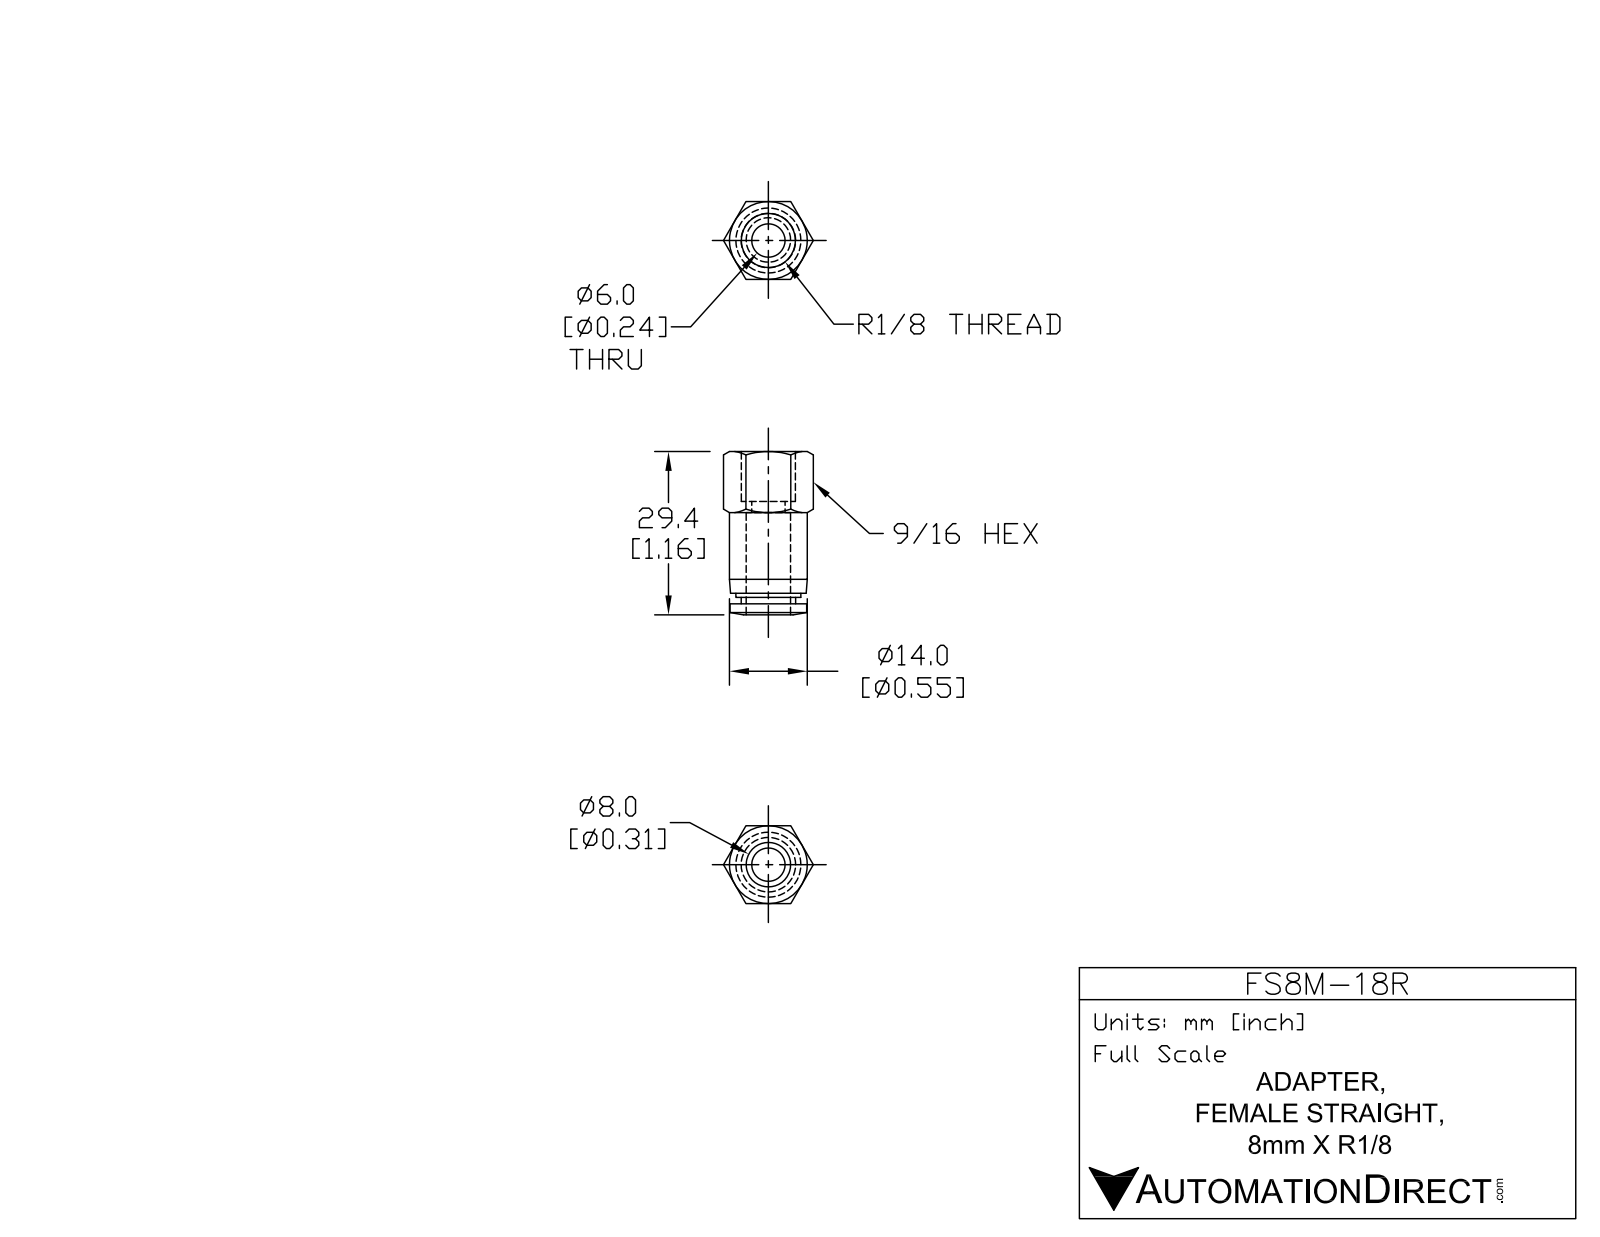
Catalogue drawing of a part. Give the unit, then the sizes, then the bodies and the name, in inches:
Units: inches
Overall size (bounding box): 1.157 × 0.636 × 0.551
Round holes (diameter × count): ⌀0.236 ×1, ⌀0.327 ×1
Round bosses / shafts (diameter × count): ⌀0.551 ×1, ⌀0.543 ×1, ⌀0.461 ×1, ⌀0.386 ×1
Main face-to-face distances: 0.551, 1.079, 0.724, 1.004, 0.075, 0.354, 0.65, 1.033, 0.679, 0.03
Volume: 0.174 in³ · Surface area: 3.849 in²
Bodies: 1 solid, 47 faces (13 planar, 12 cylindrical, 22 other)
Part name (STEP PRODUCT): FS8M-18R
STEP written by: SolidWorks 2015 (AUTOMOTIVE_DESIGN)
